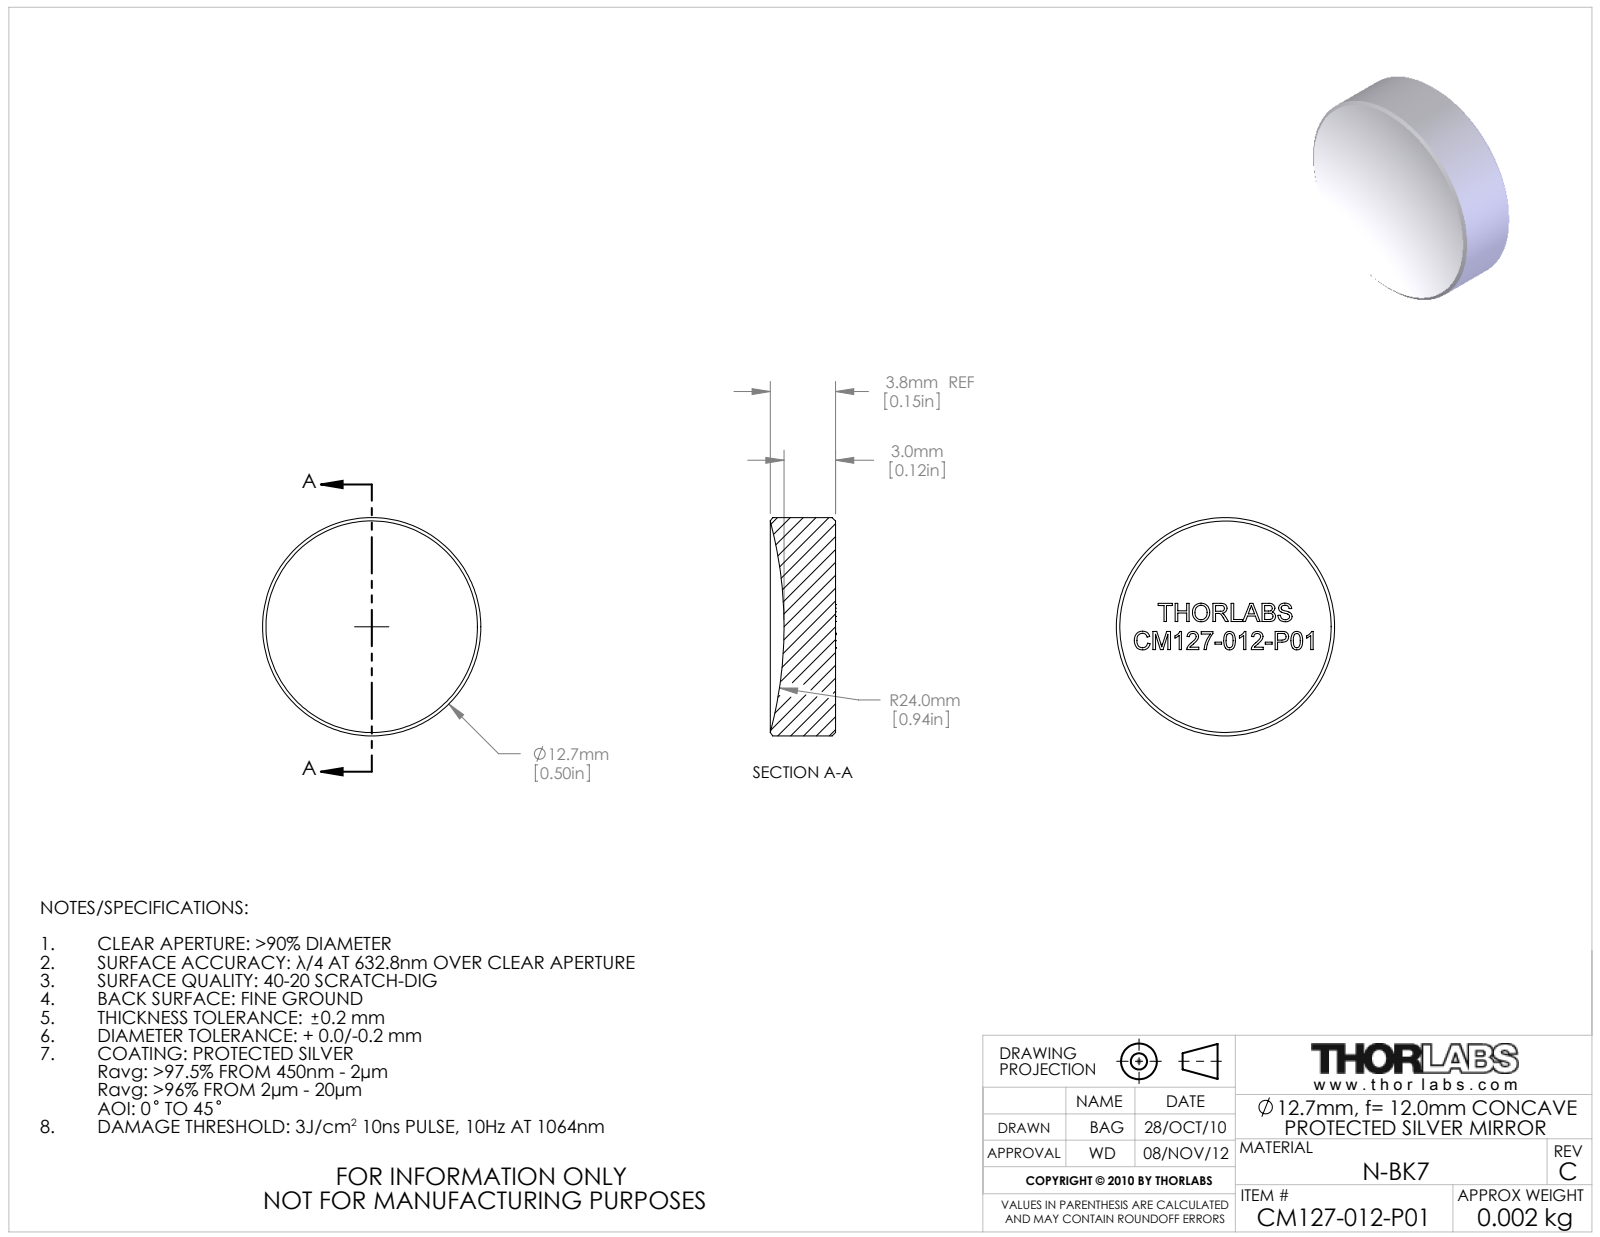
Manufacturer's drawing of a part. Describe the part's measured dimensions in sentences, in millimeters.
The part is named "17564-E0W". Its 3-D file was written by "SolidWorks 2009 (AUTOMOTIVE_DESIGN)". It is 1 solid with 261 faces: 148 planar, 2 cylindrical and 111 other. Overall it measures 12.7 by 12.7 by 3.8 millimeters. Its volume is 430 cubic millimeters and its surface area 399 square millimeters. Round bosses or shafts: 1 of diameter 12.7. The main face-to-face distances are 1.1, 0.9, 1.3, 1.6, 0.6, 3.9, 0.6, 0.9, 0.7, 1.
